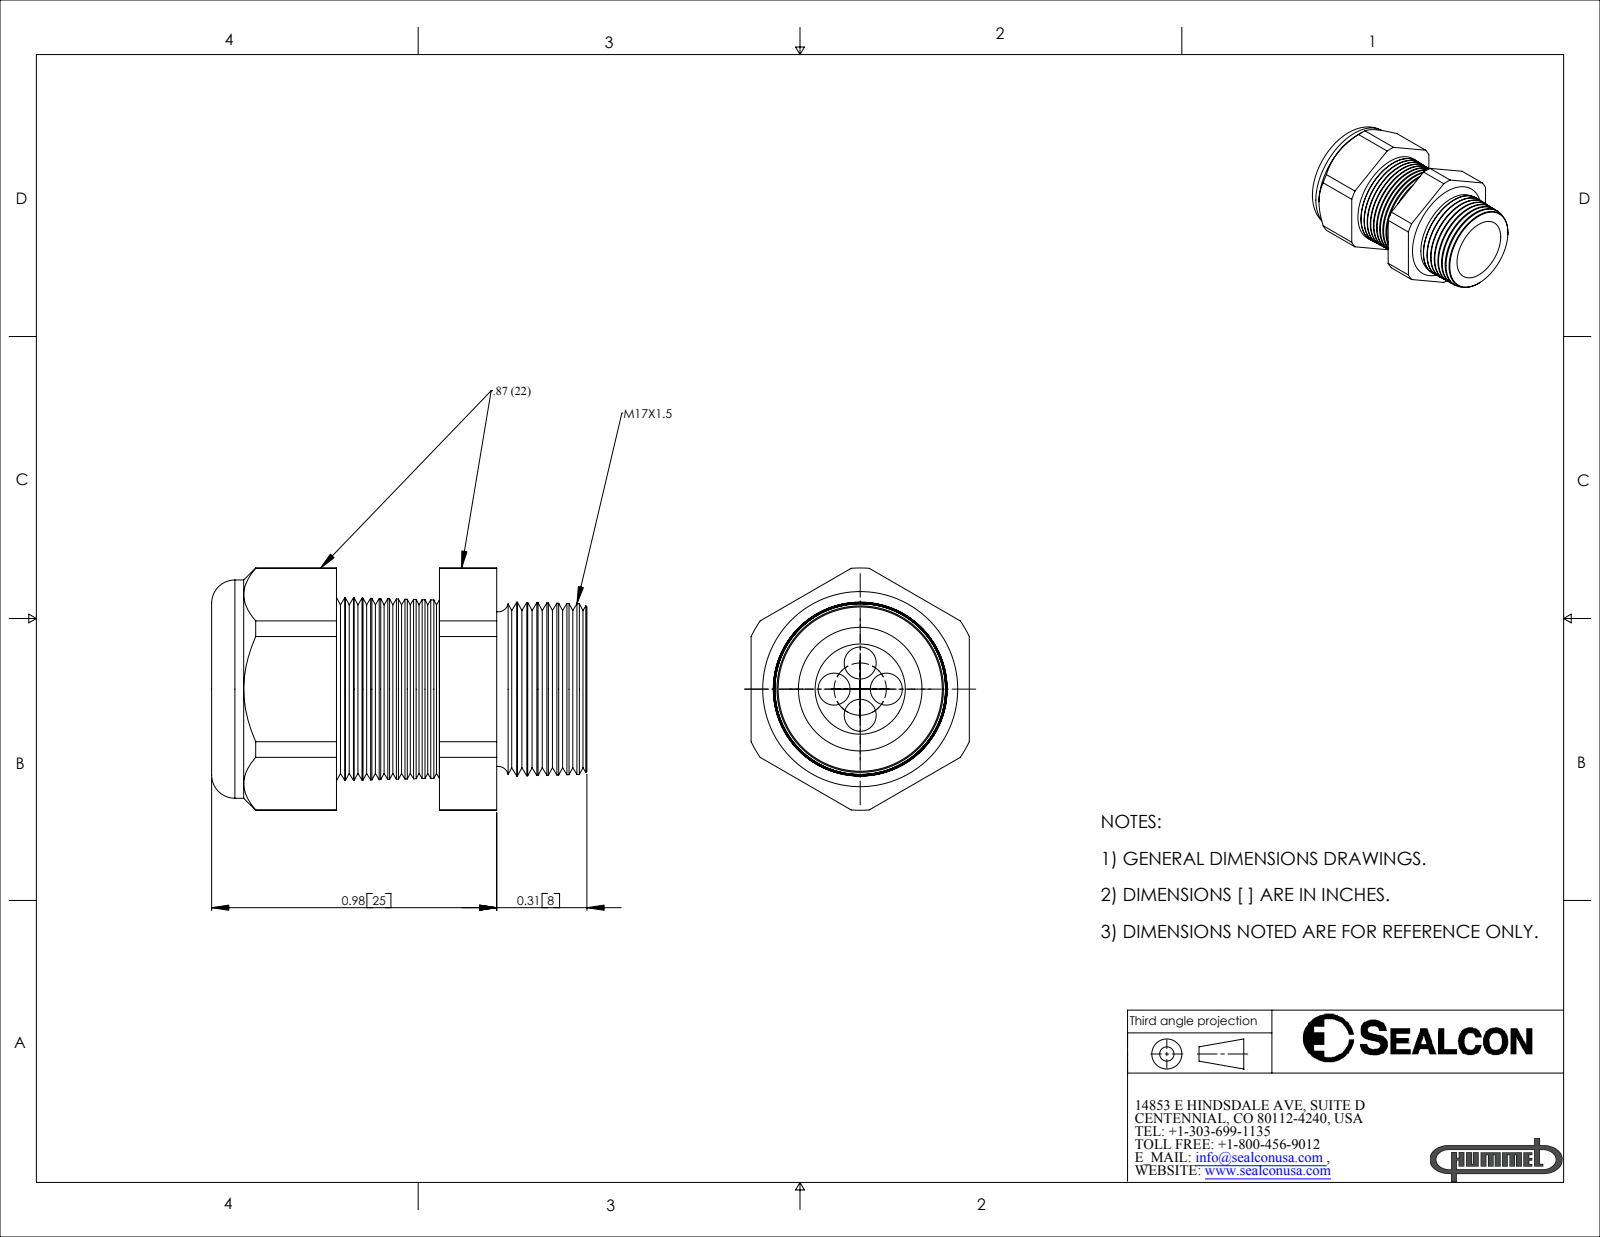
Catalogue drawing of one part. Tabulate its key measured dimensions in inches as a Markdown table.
| quantity | value |
| --- | --- |
| part name | CD17M5-BK |
| STEP written by | SolidWorks 2007 (CONFIG_CONTROL_DESIGN) |
| units | inches |
| bodies | 2 solids, 187 faces (21 planar, 28 cylindrical, 138 other) |
| overall size | 1.29 × 0.833 × 0.75 |
| volume | 0.352 in³ |
| surface area | 6.703 in² |
| round holes (diameter × count) | 0.11 × 4, 0.29 × 1, 0.31 × 1 |
| round bosses / shafts (diameter × count) | 0.75 × 1 |
| partial cylindrical surfaces (radius × count) | 0.416 × 1 |
| main face-to-face distances | 0.75, 0.75, 0.783, 0.429, 0.354, 0.98, 0.551, 0.197, 1.29, 0.861 |
| hole center spacings | 0.09, 0.127, 0.18 |
